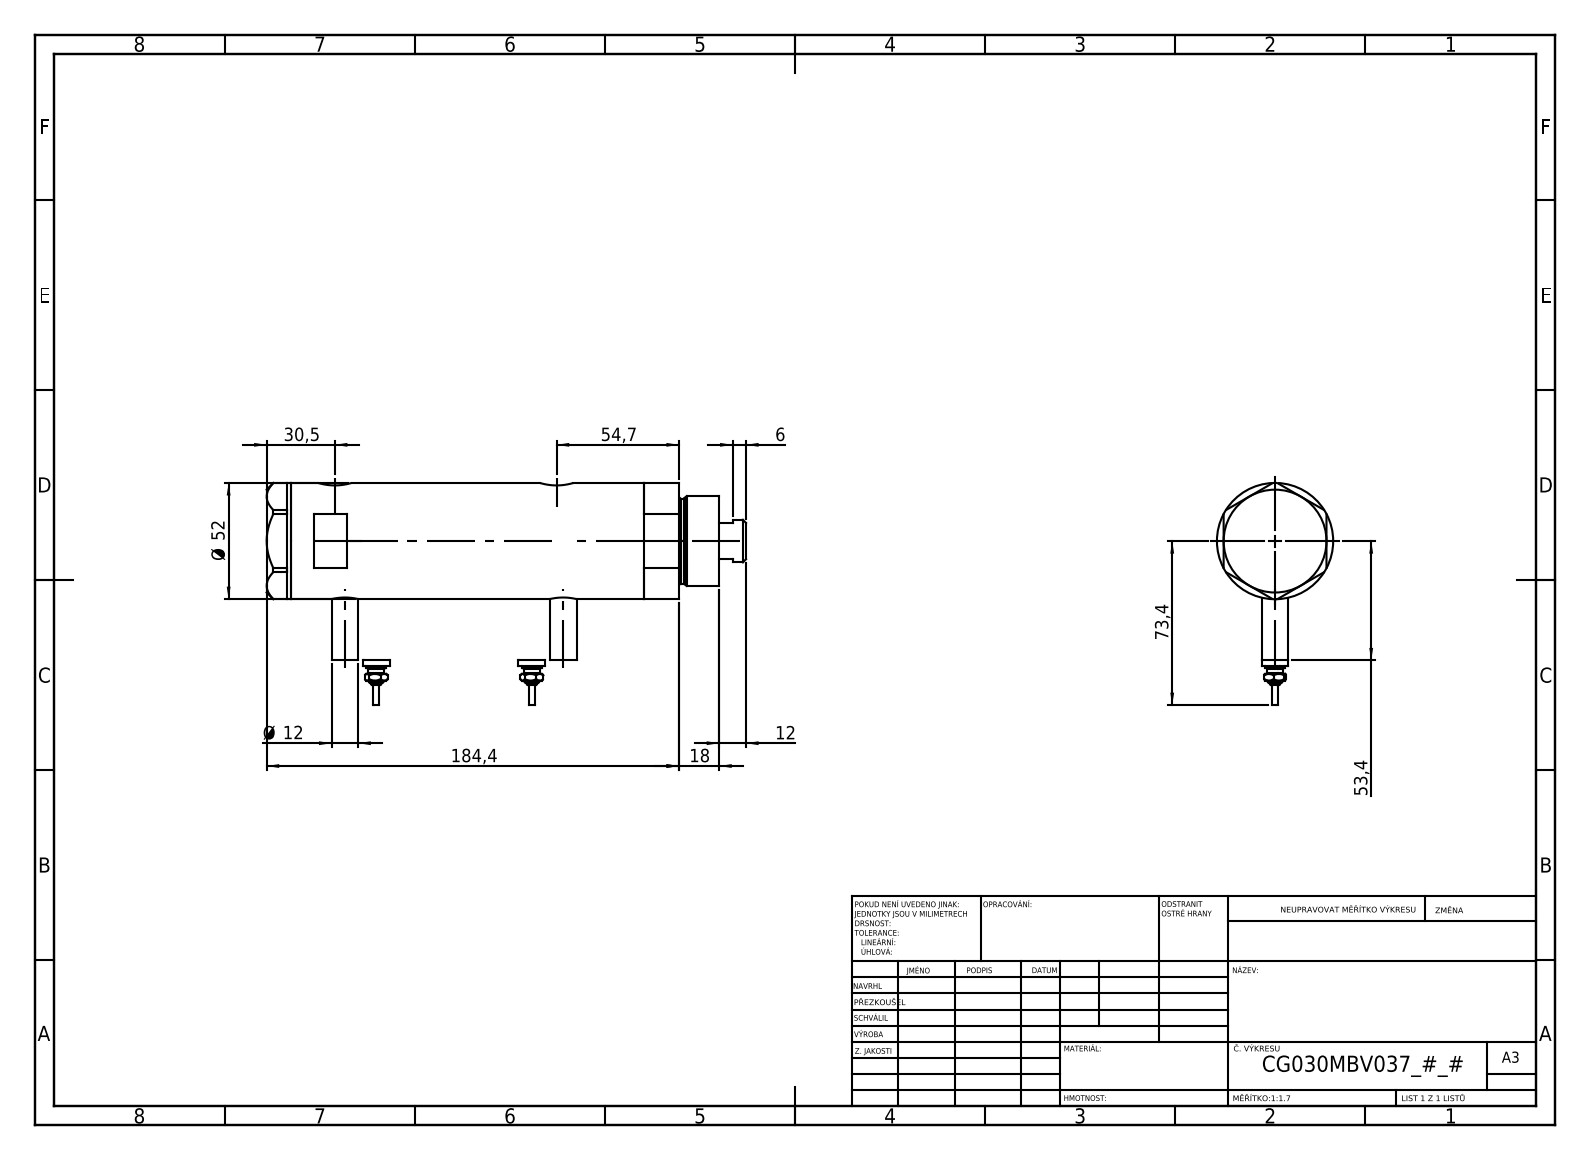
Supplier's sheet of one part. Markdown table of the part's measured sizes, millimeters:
| quantity | value |
| --- | --- |
| part name | V270CG_VC; V270CG_BACK; V270CG_FRONT; Switch (+1 more) |
| STEP written by | SolidWorks 2019 (CONFIG_CONTROL_DESIGN) |
| units | millimeters |
| bodies | 6 solids, 226 faces (93 planar, 69 cylindrical, 64 other) |
| overall size | 214.4 × 99.4 × 52 |
| volume | 401 897 mm³ |
| surface area | 90 249 mm² |
| round holes (diameter × count) | 9.73 × 2, 12.5 × 2, 15 × 2, 6.5 × 1, 20 × 1, 21.5 × 1, 30 × 1, 33 × 1, 44 × 1 |
| round bosses / shafts (diameter × count) | 12 × 4, 9 × 2, 7 × 2, 4.5 × 2, 2.5 × 2, 52 × 1, 40 × 1, 38 × 1 |
| main face-to-face distances | 121.5, 23.8, 97.7, 11, 34.8, 132.5, 46, 36.4, 168.9, 157.9 |
| hole center spacings | 2.9, 4.5, 94.7, 97.6, 99.2, 102.1 |
